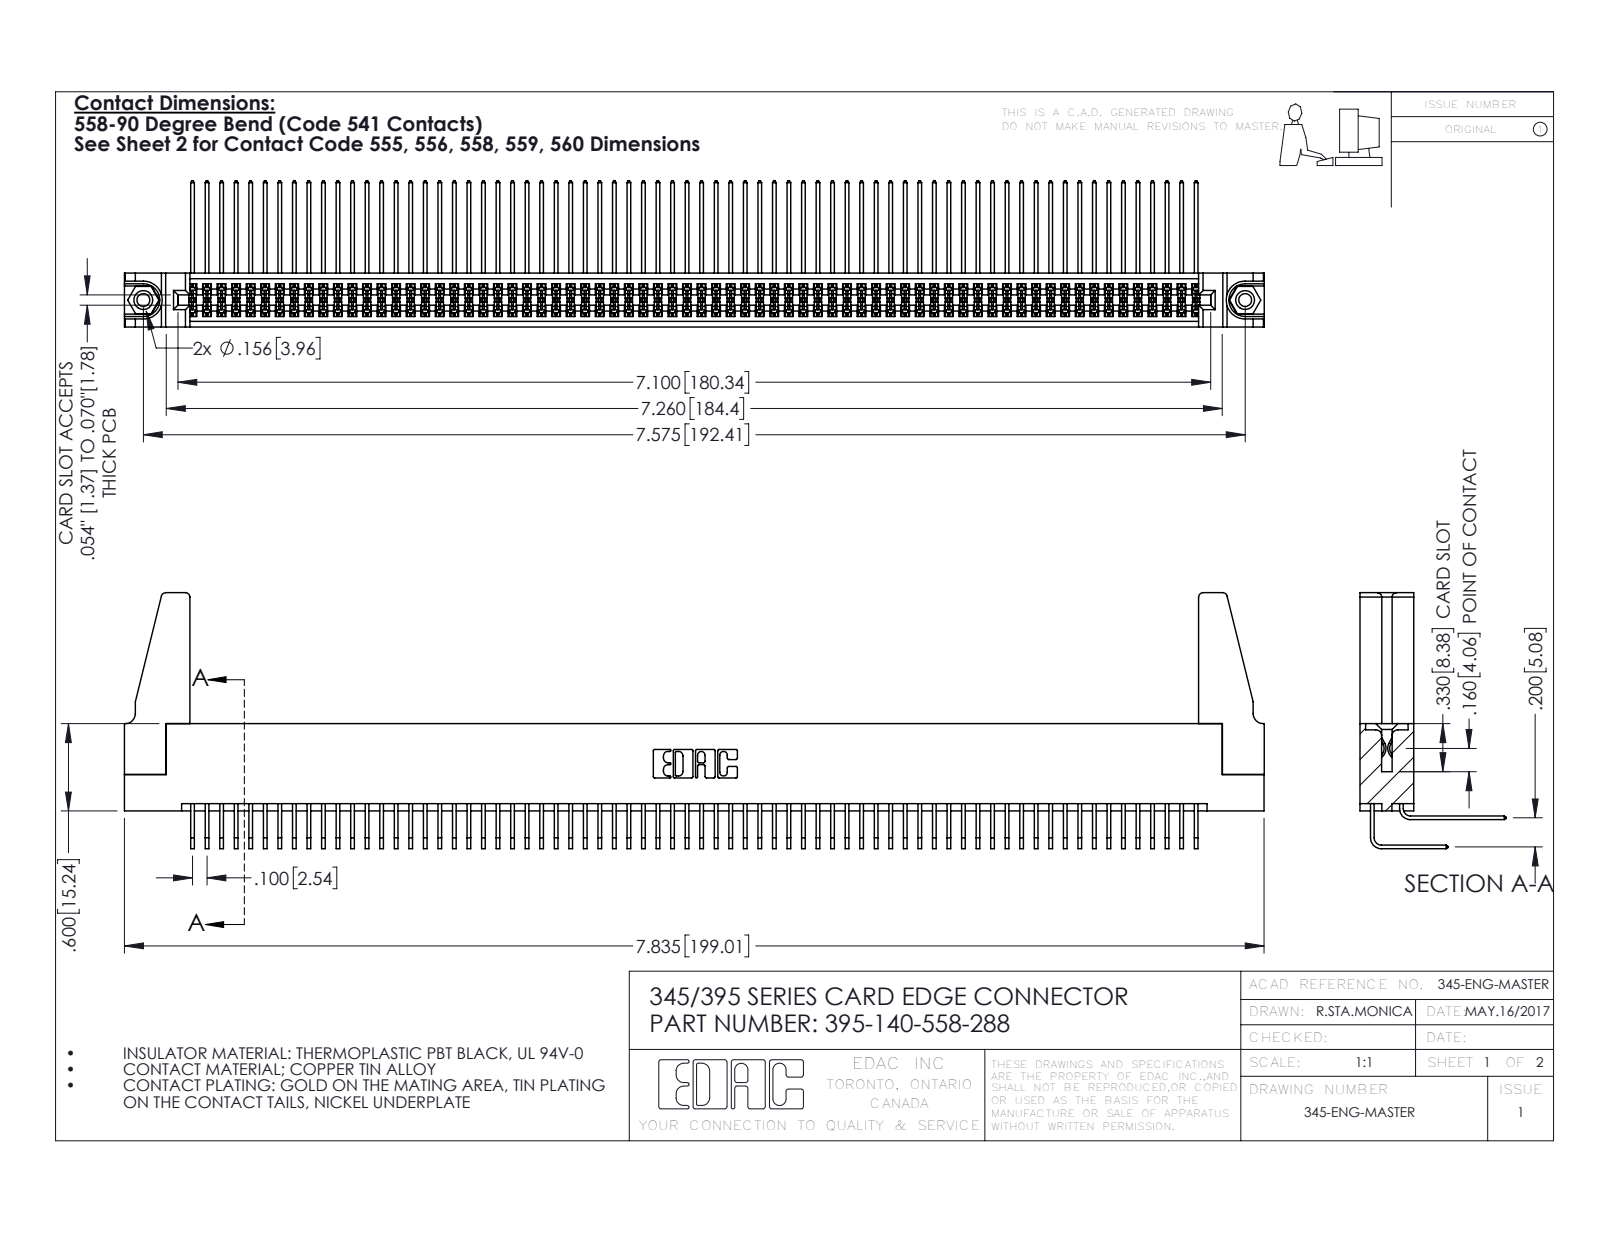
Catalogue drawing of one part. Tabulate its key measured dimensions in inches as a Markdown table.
| quantity | value |
| --- | --- |
| part name | 345-292-001_558 Tail - 2; 345 Part_Flush Mounting Lugs - 0.156 Dia-TH; 345-220-078_345-220-088; 395-140-558-288 (+2 more) |
| STEP written by | SolidWorks 2016 (CONFIG_CONTROL_DESIGN) |
| units | inches |
| bodies | 145 solids, 7530 faces (5052 planar, 2462 cylindrical, 16 other) |
| overall size | 7.836 × 1.759 × 1.005 |
| volume | 1.443 in³ |
| surface area | 58.31 in² |
| round holes (diameter × count) | 0.089 × 2, 0.125 × 2, 0.156 × 2, 0.064 × 1 |
| round bosses / shafts (diameter × count) | 0.155 × 2 |
| partial cylindrical surfaces (radius × count) | 0.006 × 279, 0.01 × 22, 0.03 × 8, 0.007 × 6, 0.031 × 6, 0.026 × 3, 0.014 × 2, 0.019 × 2 |
| main face-to-face distances | 0.072, 0.298, 0.2, 0.37, 0.098, 0.272, 0.025, 0.225, 0.025, 0.175 |
| hole center spacings | 0.27, 7.339, 7.575 |
